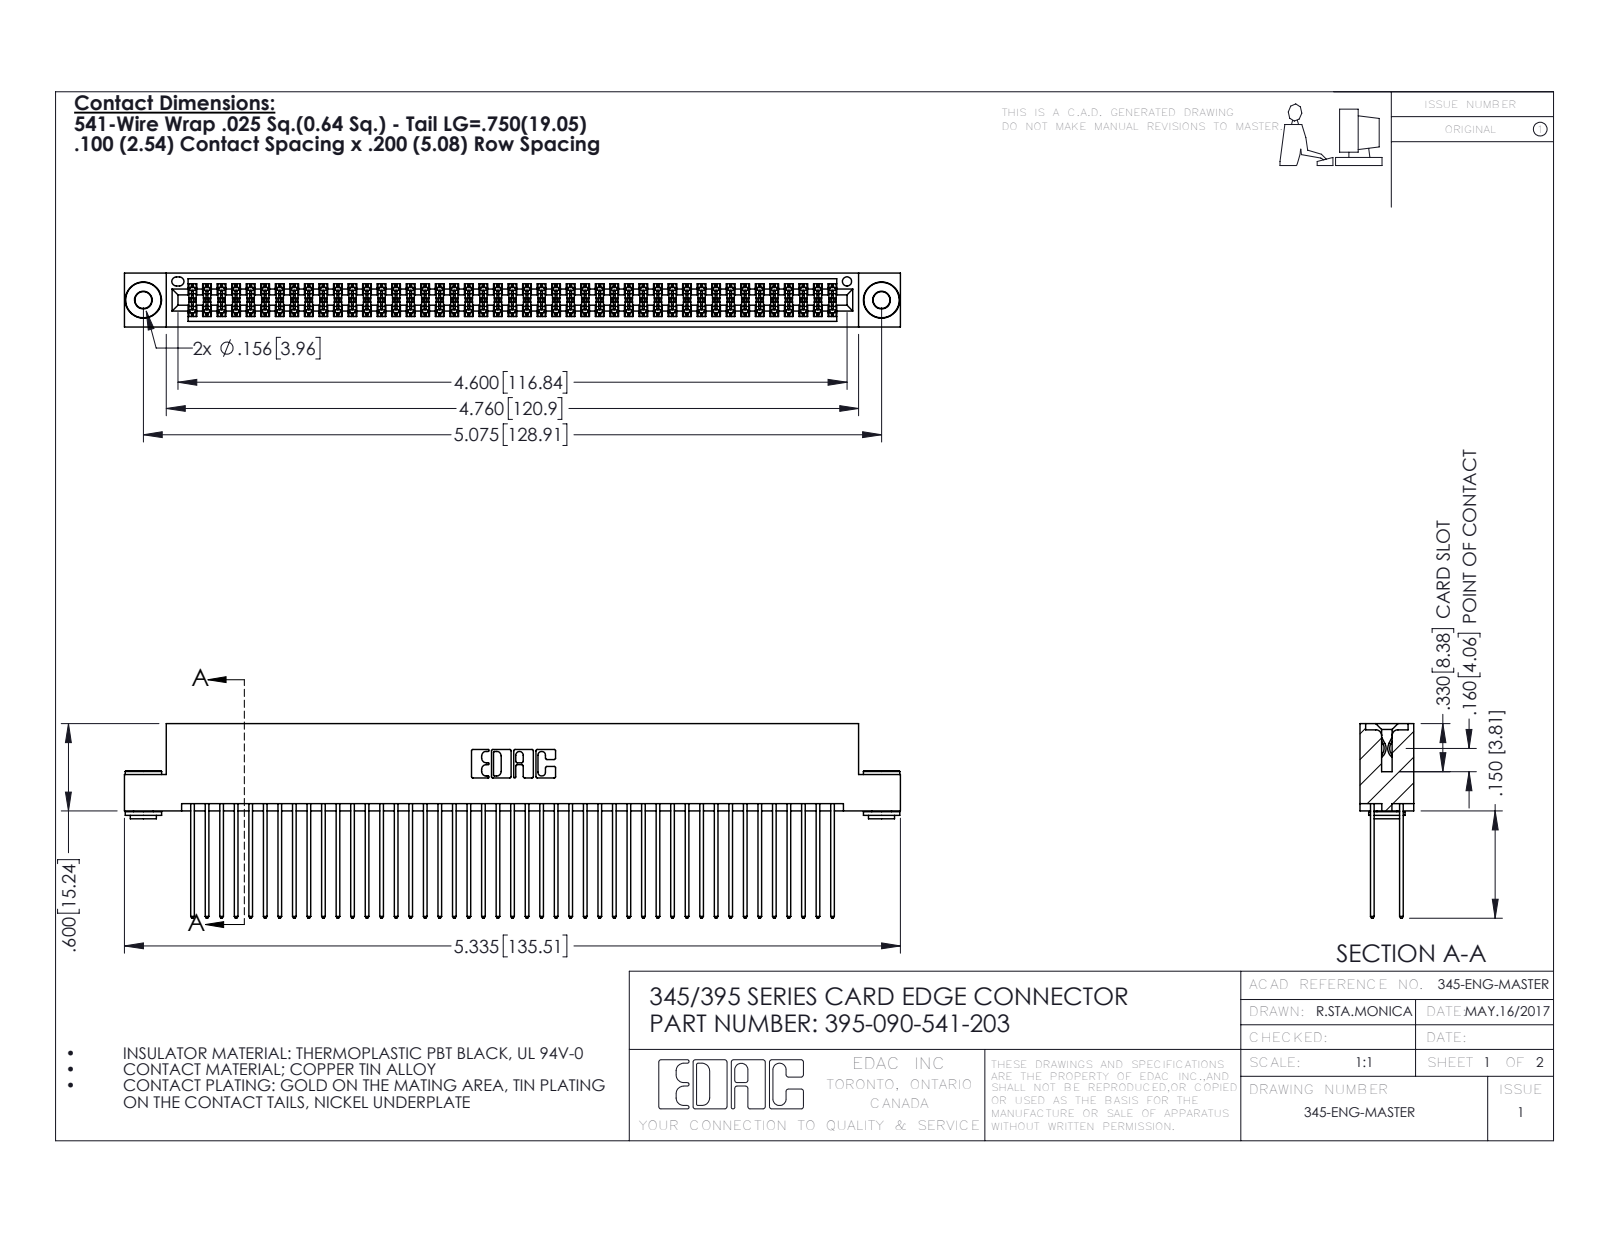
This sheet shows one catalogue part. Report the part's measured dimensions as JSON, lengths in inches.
{"part_name": "395-090-541-203; 345 Part_Flush Mounting Lugs - 0.156 Dia-TH; 345-250-002_345-250-002-102; 345-292-001_345-293-141", "step_written_by": "SolidWorks 2016 (CONFIG_CONTROL_DESIGN)", "units": "inches", "bodies": {"solids": 93, "faces": 4664, "planar": 3060, "cylindrical": 1596, "other": 8}, "overall_size": [5.335, 1.337, 0.37], "volume_in3": 0.838, "surface_area_in2": 35.62, "round_holes": [[0.116, 2], [0.156, 2], [0.064, 1]], "round_bosses_or_shafts": [[0.25, 2], [0.18, 2], [0.136, 2]], "partial_cylinders_radius": [[0.006, 135], [0.01, 90], [0.01, 22], [0.007, 6], [0.031, 6], [0.026, 3], [0.014, 2], [0.019, 2]], "face_to_face_distances": [0.072, 0.298, 0.2, 0.025, 0.098, 0.272, 0.225, 0.37, 0.175, 0.149], "hole_center_spacings": [0.27, 4.839, 5.075]}
